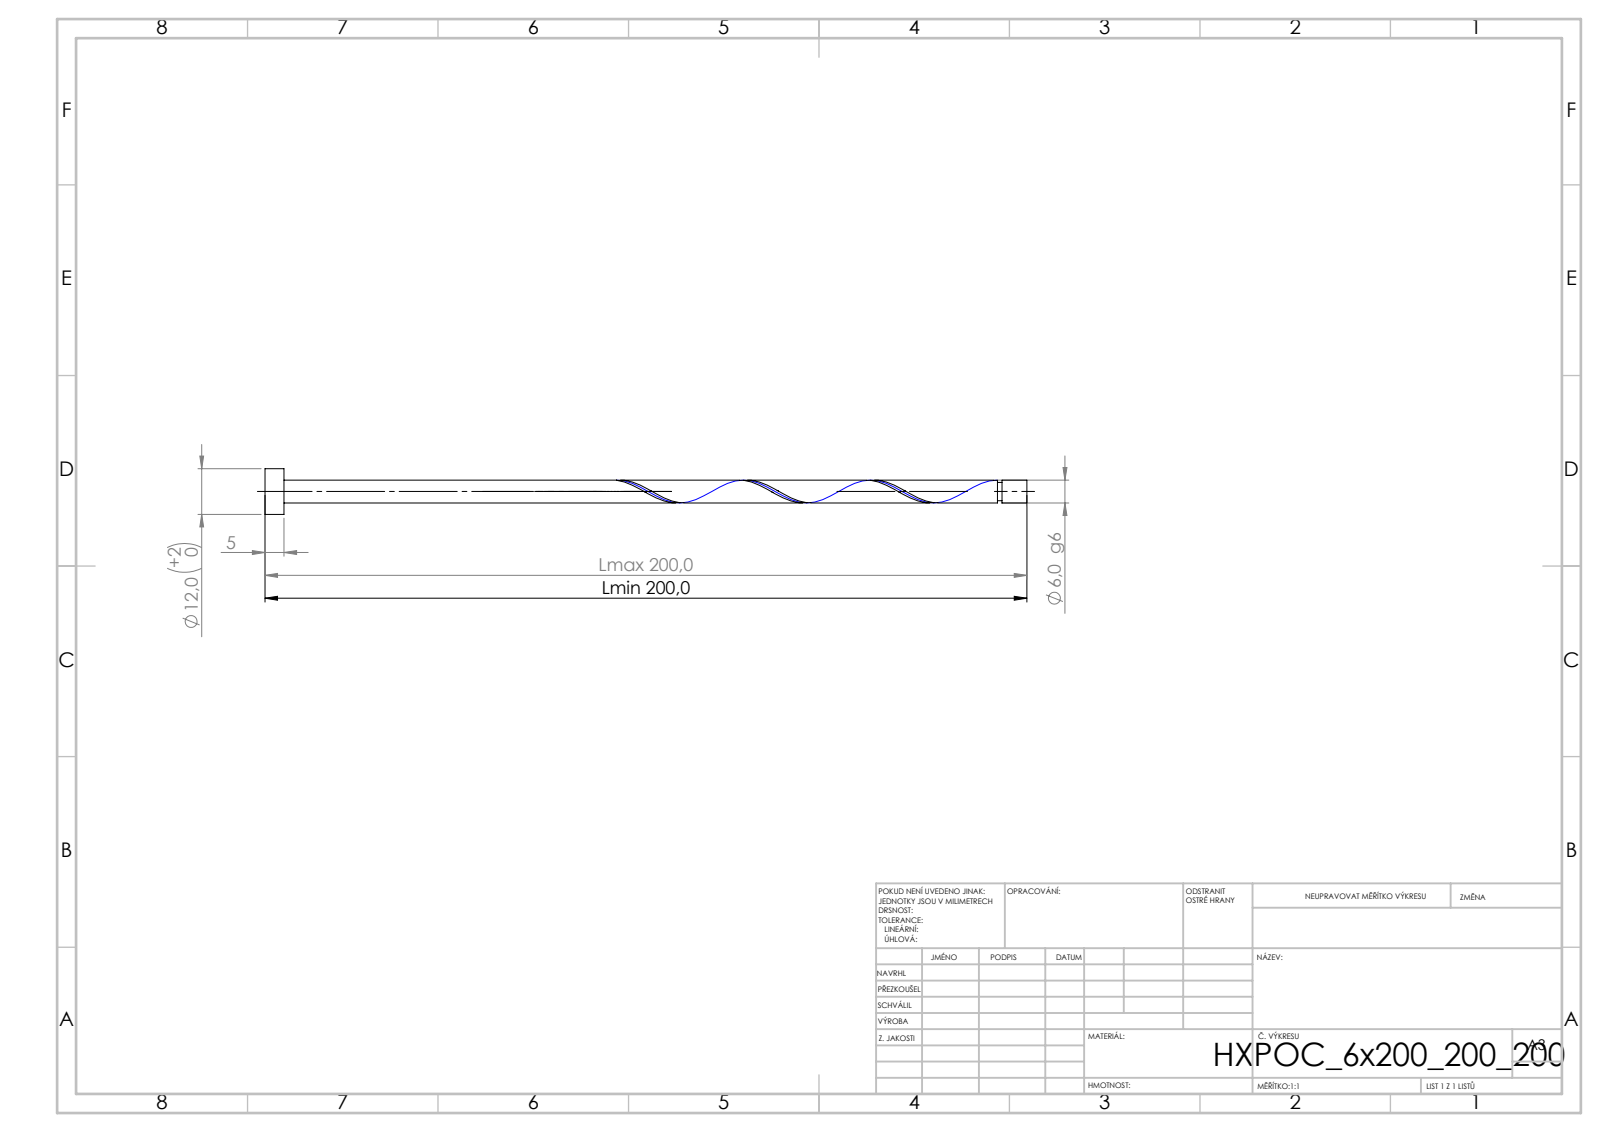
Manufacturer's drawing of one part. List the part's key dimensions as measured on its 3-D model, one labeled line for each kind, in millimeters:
STEP written by: SolidWorks 2019 (CONFIG_CONTROL_DESIGN)
Units: millimetres
Bodies: 1 solid, 21 faces (6 planar, 14 cylindrical, 1 other)
Overall size (bounding box): 200 × 12 × 12
Volume: 6 013 mm³ · Surface area: 4 175 mm²
Round bosses / shafts (diameter × count): ⌀12 ×1, ⌀6 ×1, ⌀4.8 ×1
Main face-to-face distances: 5, 200, 195, 193.46, 188.46, 6.54, 192.26, 187.26, 1.2, 7.74
